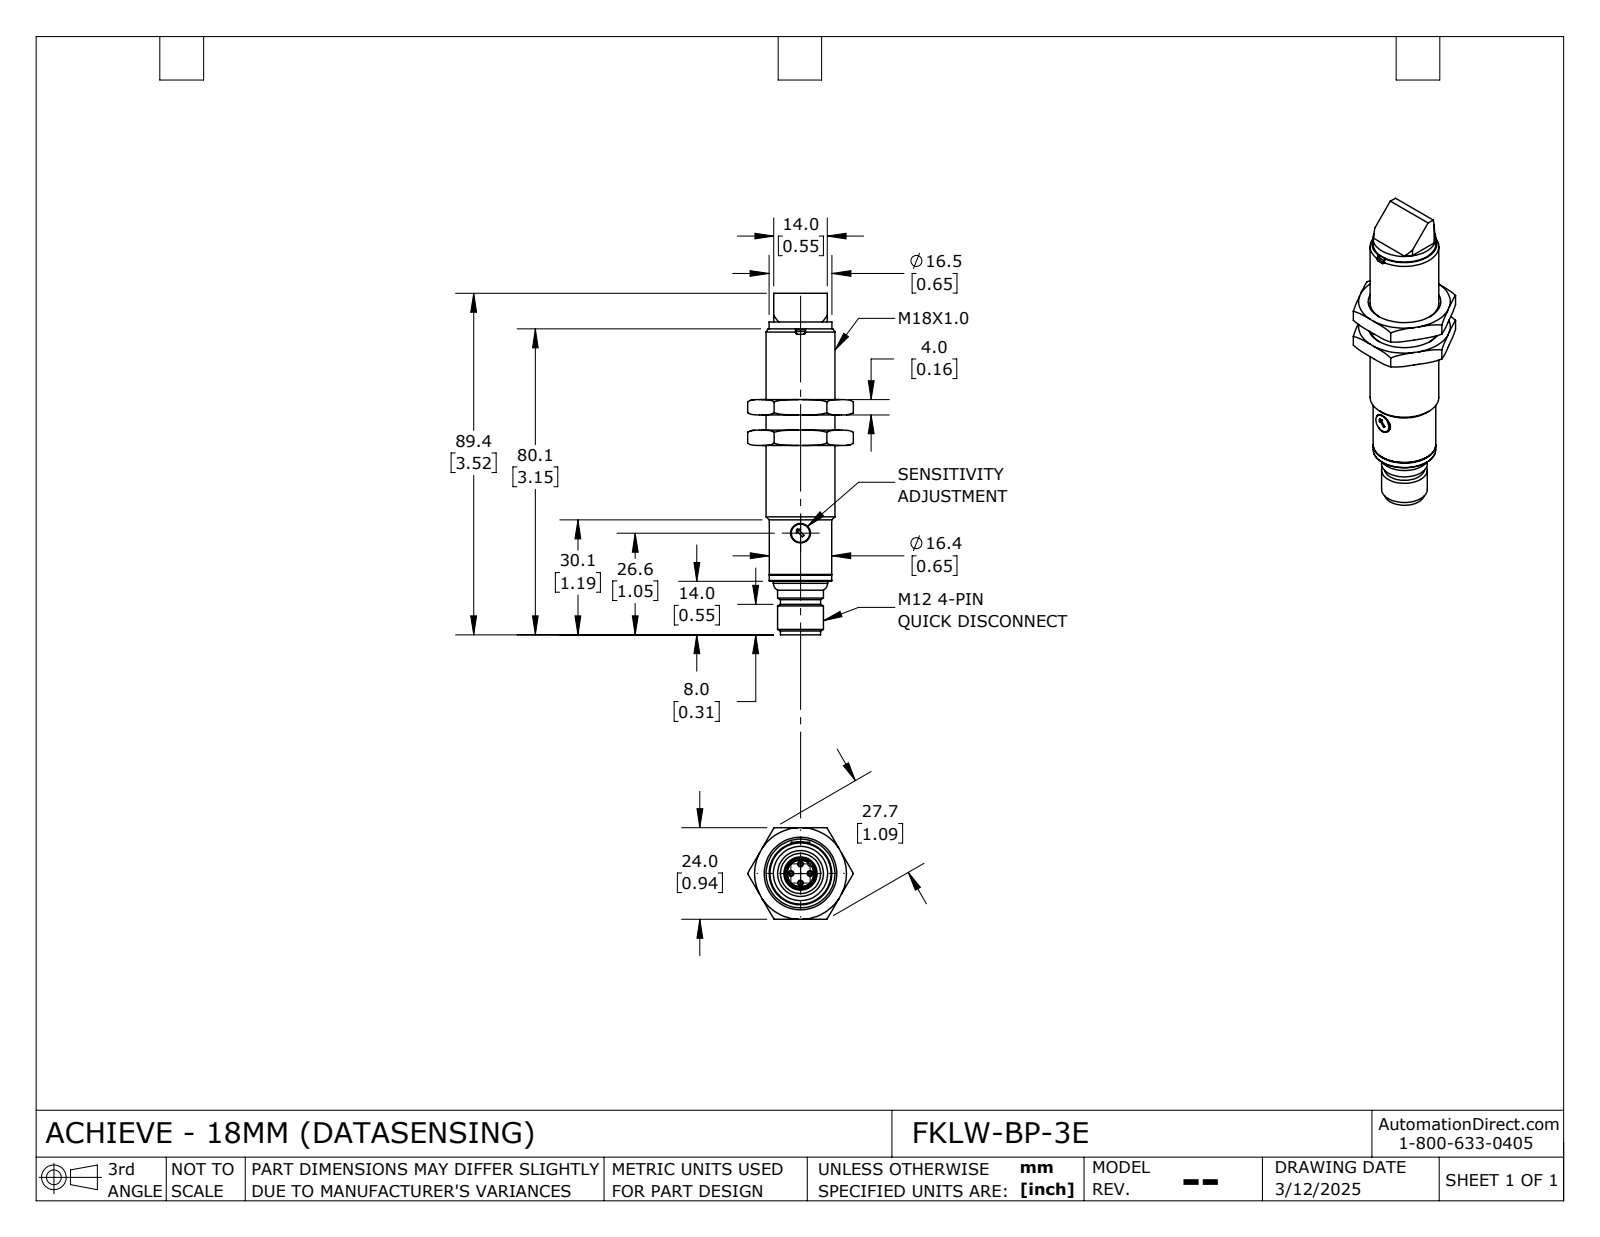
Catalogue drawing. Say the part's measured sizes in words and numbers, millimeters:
The part is named "FKLW-BP-3E_Default". Its 3-D file was written by "SolidWorks 2024 (CONFIG_CONTROL_DESIGN)". It is 4 solids with 155 faces: 67 planar, 35 cylindrical and 53 other. Overall it measures 89.4 by 27.7 by 24 millimeters. Its volume is 20 170 cubic millimeters and its surface area 8 800 square millimeters. Round holes: 1 of diameter 2.7, 1 of diameter 4.7, 1 of diameter 7.1, 1 of diameter 8.3, 1 of diameter 15, 1 of diameter 15.8, 1 of diameter 18. Round bosses or shafts: 4 of diameter 1, 1 of diameter 16.5, 1 of diameter 16.4, 1 of diameter 14.2, 1 of diameter 12, 1 of diameter 10.5, 1 of diameter 7, 1 of diameter 4.8. Partial cylindrical surfaces (rounded edges, fillets, slot ends): 4 of radius 0.5, 1 of radius 0.6, 1 of radius 8.1, 1 of radius 8.4. The main face-to-face distances are 4, 8, 24, 12, 2.9, 0.4, 3.3, 2.8, 2.4, 0.5.
